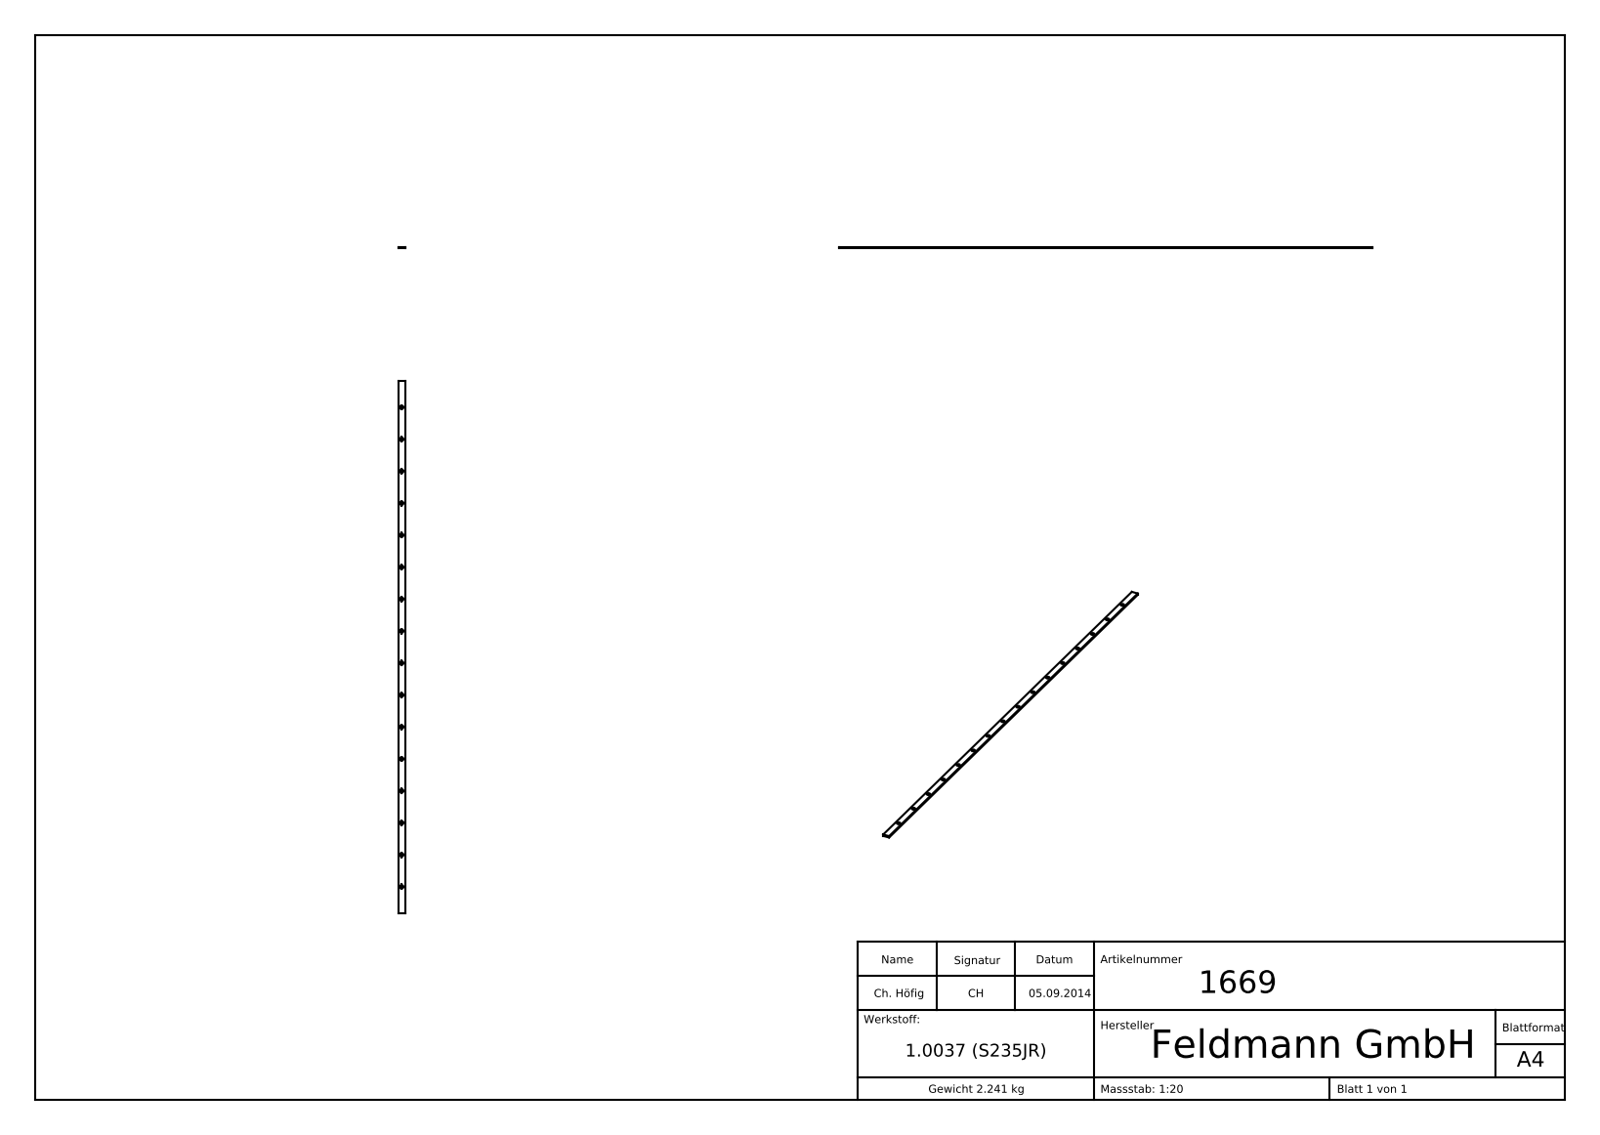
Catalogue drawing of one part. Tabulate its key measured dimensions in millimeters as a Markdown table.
| quantity | value |
| --- | --- |
| part name | 1669 |
| STEP written by | SolidWorks 2015 (CONFIG_CONTROL_DESIGN) |
| units | millimeters |
| bodies | 1 solid, 151 faces (71 planar, 32 cylindrical, 48 other) |
| overall size | 2000 × 25 × 6 |
| volume | 287 256 mm³ |
| surface area | 123 997 mm² |
| round holes (diameter × count) | 13 × 16 |
| main face-to-face distances | 6, 25, 2000, 1999.5, 0.5, 0.39, 2.97, 3, 1.12, 4.09 |
| hole center spacings | 120, 240, 360, 480, 600, 720, 840, 960 |
